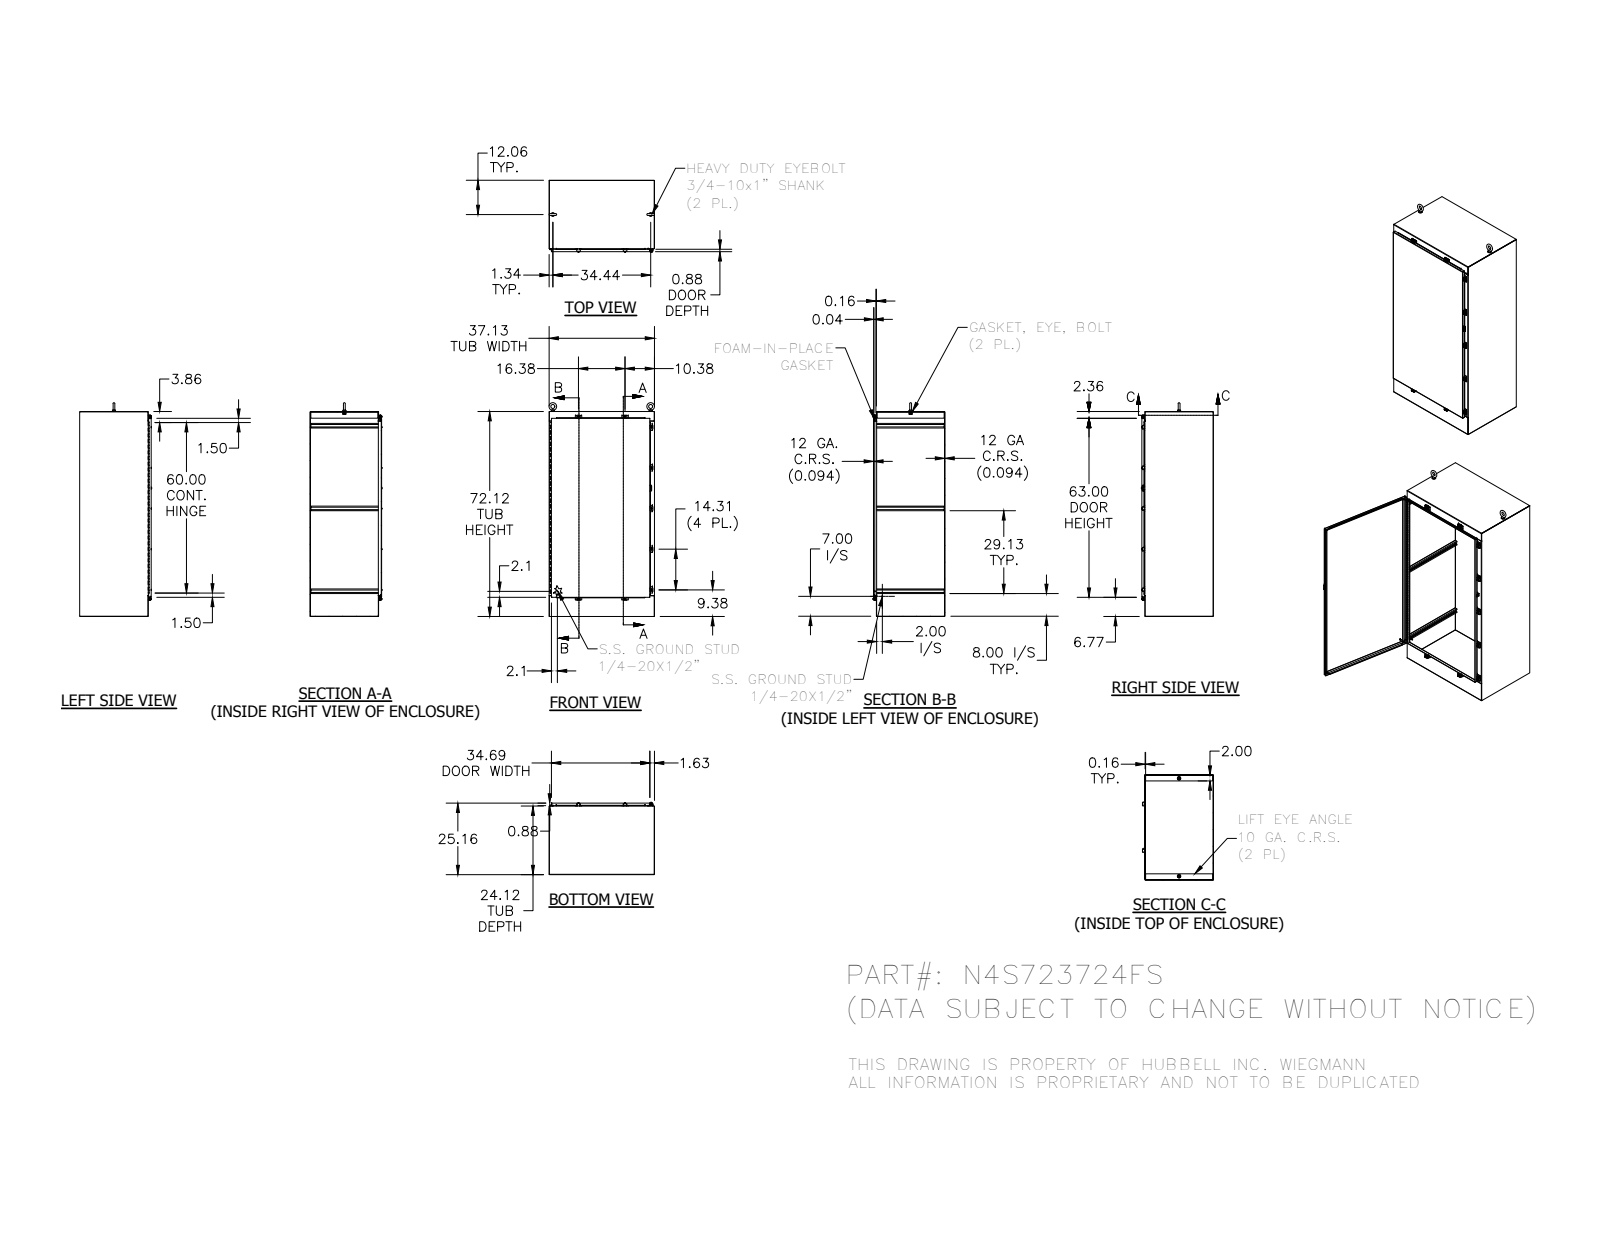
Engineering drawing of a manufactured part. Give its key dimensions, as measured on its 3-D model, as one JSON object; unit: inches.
{"part_name": "HSSN1300W60P_1; N4S7237FSDR_1; HSSN1300W60_1; 30824-1_1 (+8 more)", "step_written_by": "SolidWorks 2014 (AUTOMOTIVE_DESIGN)", "units": "inches", "bodies": {"solids": 78, "faces": 3000, "planar": 1210, "cylindrical": 1210, "other": 580}, "overall_size": [75.248, 37.125, 25.355], "volume_in3": 1230, "surface_area_in2": 25407, "round_holes": [[0.211, 9], [0.281, 9], [0.3, 9], [0.11, 3], [0.642, 2], [0.813, 2], [0.125, 1], [0.156, 1], [0.5, 1]], "round_bosses_or_shafts": [[0.25, 12], [0.52, 9], [0.5, 9], [0.35, 9], [1.25, 2], [1.12, 2], [0.75, 2], [0.337, 2]], "partial_cylinders_radius": [[0.03, 107], [0.125, 43], [0.062, 22], [0.25, 21], [0.031, 19], [0.019, 18], [0.053, 18], [0.086, 18]], "face_to_face_distances": [0.094, 25.067, 37.031, 24.973, 25.161, 36.938, 72.031, 37.125, 24.031, 1.035], "hole_center_spacings": [14.313, 28.626, 0.789, 16.38, 42.939, 64.375, 66.426, 0.449]}
